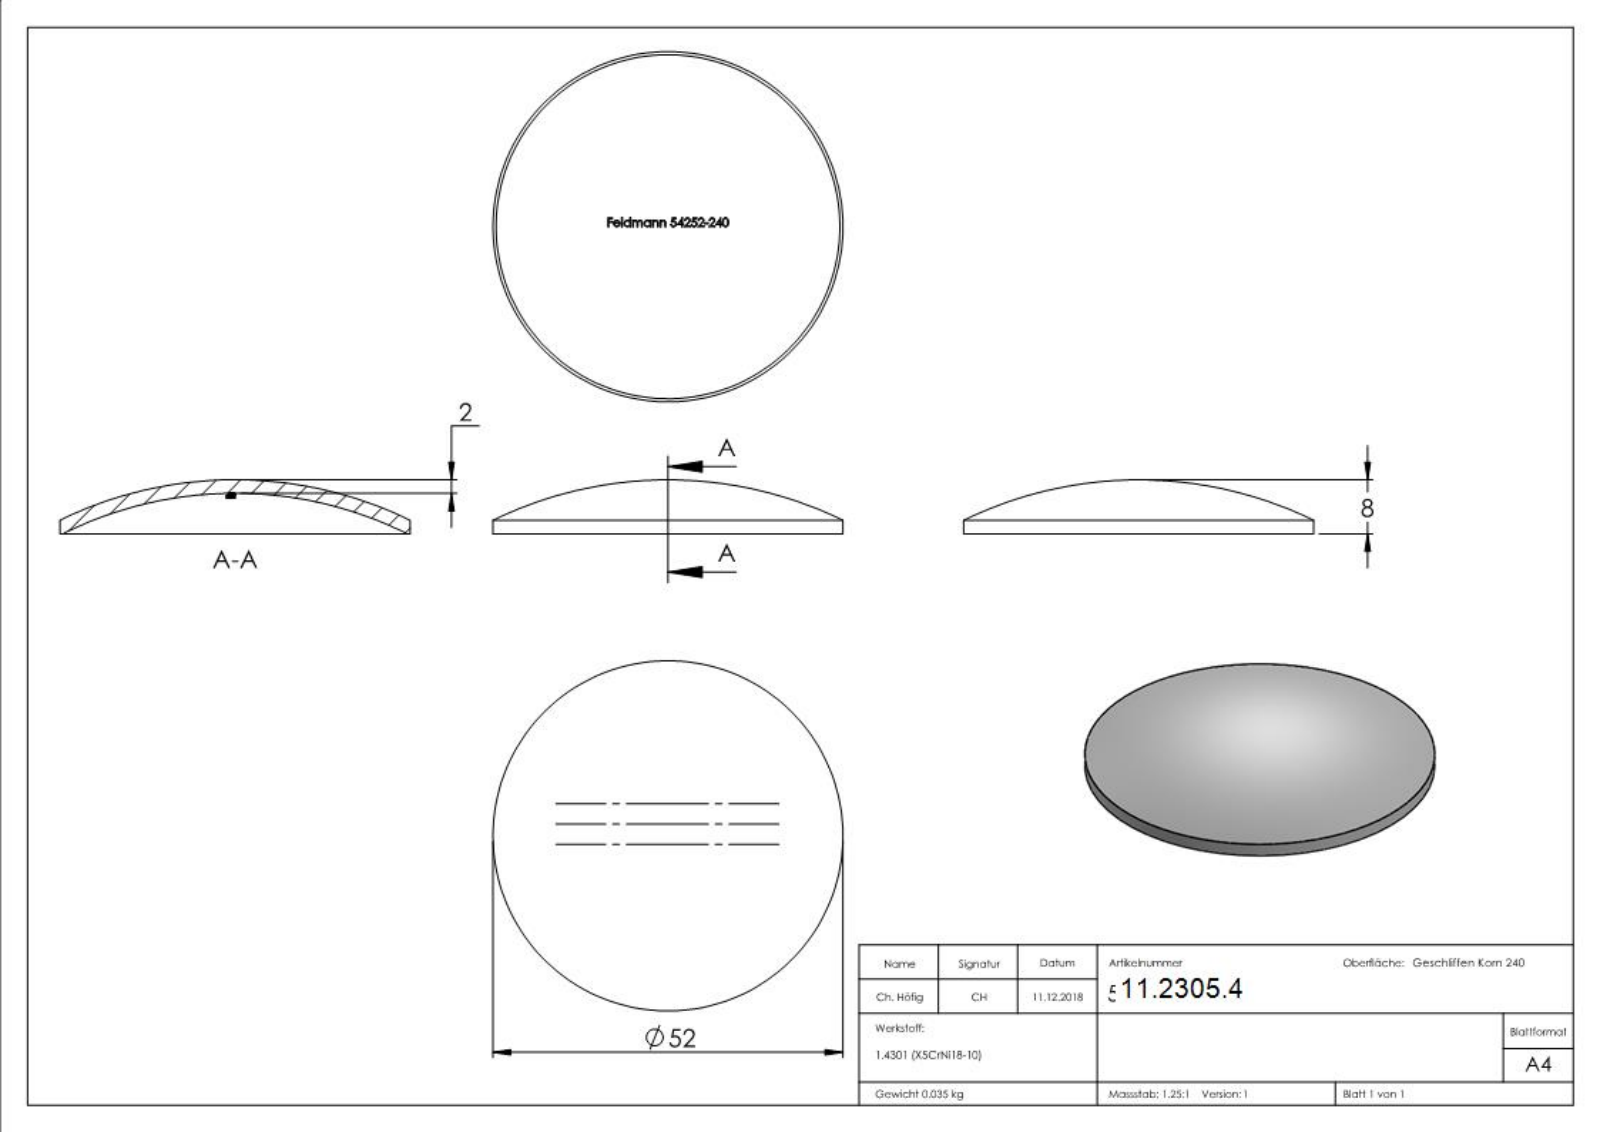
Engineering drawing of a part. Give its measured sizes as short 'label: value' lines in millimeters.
name: 54252-240
written by: SolidWorks 2015 (CONFIG_CONTROL_DESIGN)
unit: mm
bodies: 1 solid, 247 faces (115 planar, 2 cylindrical, 130 other)
size: 52 × 52 × 8
volume: 4 473 mm³; area: 4 810 mm²
bosses: 1× ⌀52
face distances: 0.44, 0.88, 2.97, 1.32, 1.19, 0.39, 4.7, 14.62, 7.67, 10.94
